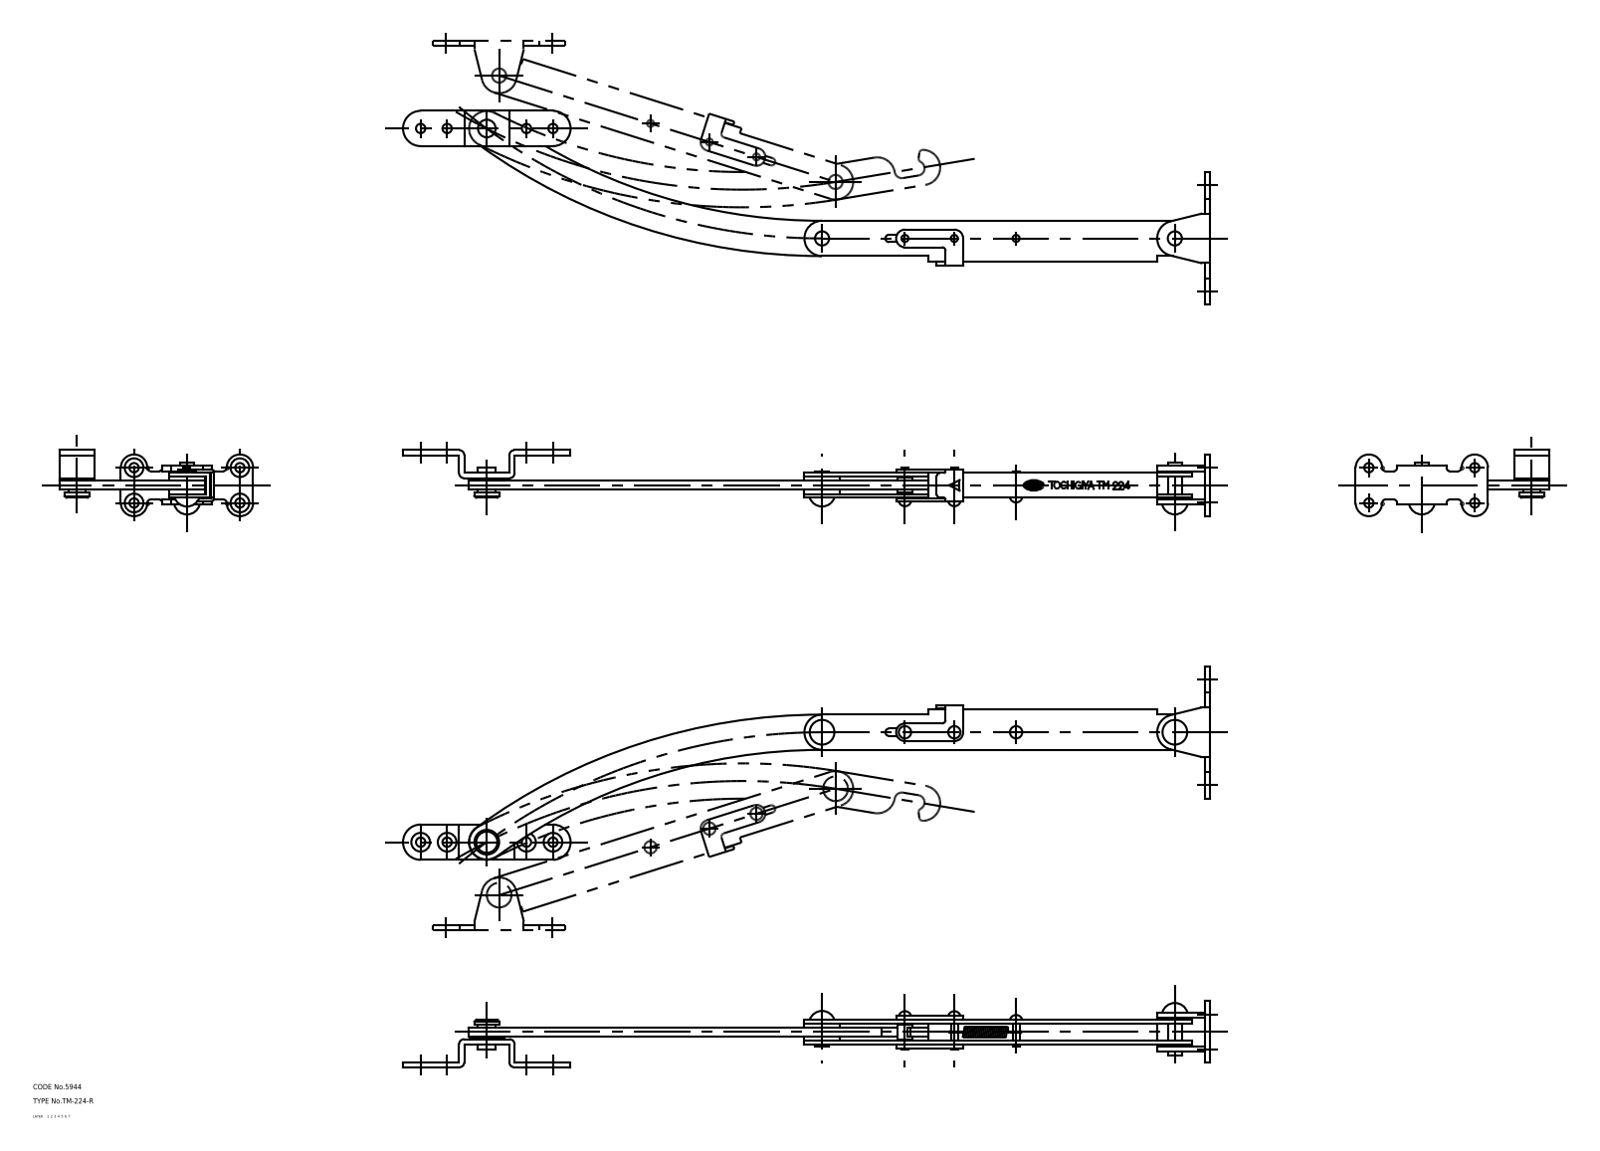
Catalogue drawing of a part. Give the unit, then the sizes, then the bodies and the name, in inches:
Units: inches
Overall size (bounding box): 18.013 × 4.324 × 1.476
Round holes (diameter × count): ⌀0.209 ×8, ⌀0.157 ×2, ⌀0.161 ×2, ⌀0.315 ×2, ⌀0.319 ×2, ⌀0.394 ×1
Round bosses / shafts (diameter × count): ⌀0.787 ×3, ⌀0.551 ×1, ⌀0.315 ×1, ⌀0.157 ×1
Partial cylindrical surfaces — rounded edges, fillets, slot ends (radius × count): R0.079 ×15, R0.118 ×6, R0.394 ×5, R0.295 ×4, R0.004 ×2, R0.039 ×2, R0.083 ×2, R0.161 ×2
Main face-to-face distances: 0.079, 0.472, 0.177, 0.374, 0.295, 0.098, 0.118, 0.197, 0.394, 0.551
Hole centre spacings: 2.362, 0.591, 0.787, 0.886, 1.476, 2.49, 2.953, 7.874
Volume: 4.243 in³ · Surface area: 91.03 in²
Bodies: 18 solids, 314 faces (99 planar, 149 cylindrical, 66 other)
Part name (STEP PRODUCT): rivet_C_mr; spring_mr; spacer_B_mr; arm_B_mr (+8 more)
STEP written by: SolidWorks 2015 (AUTOMOTIVE_DESIGN)
